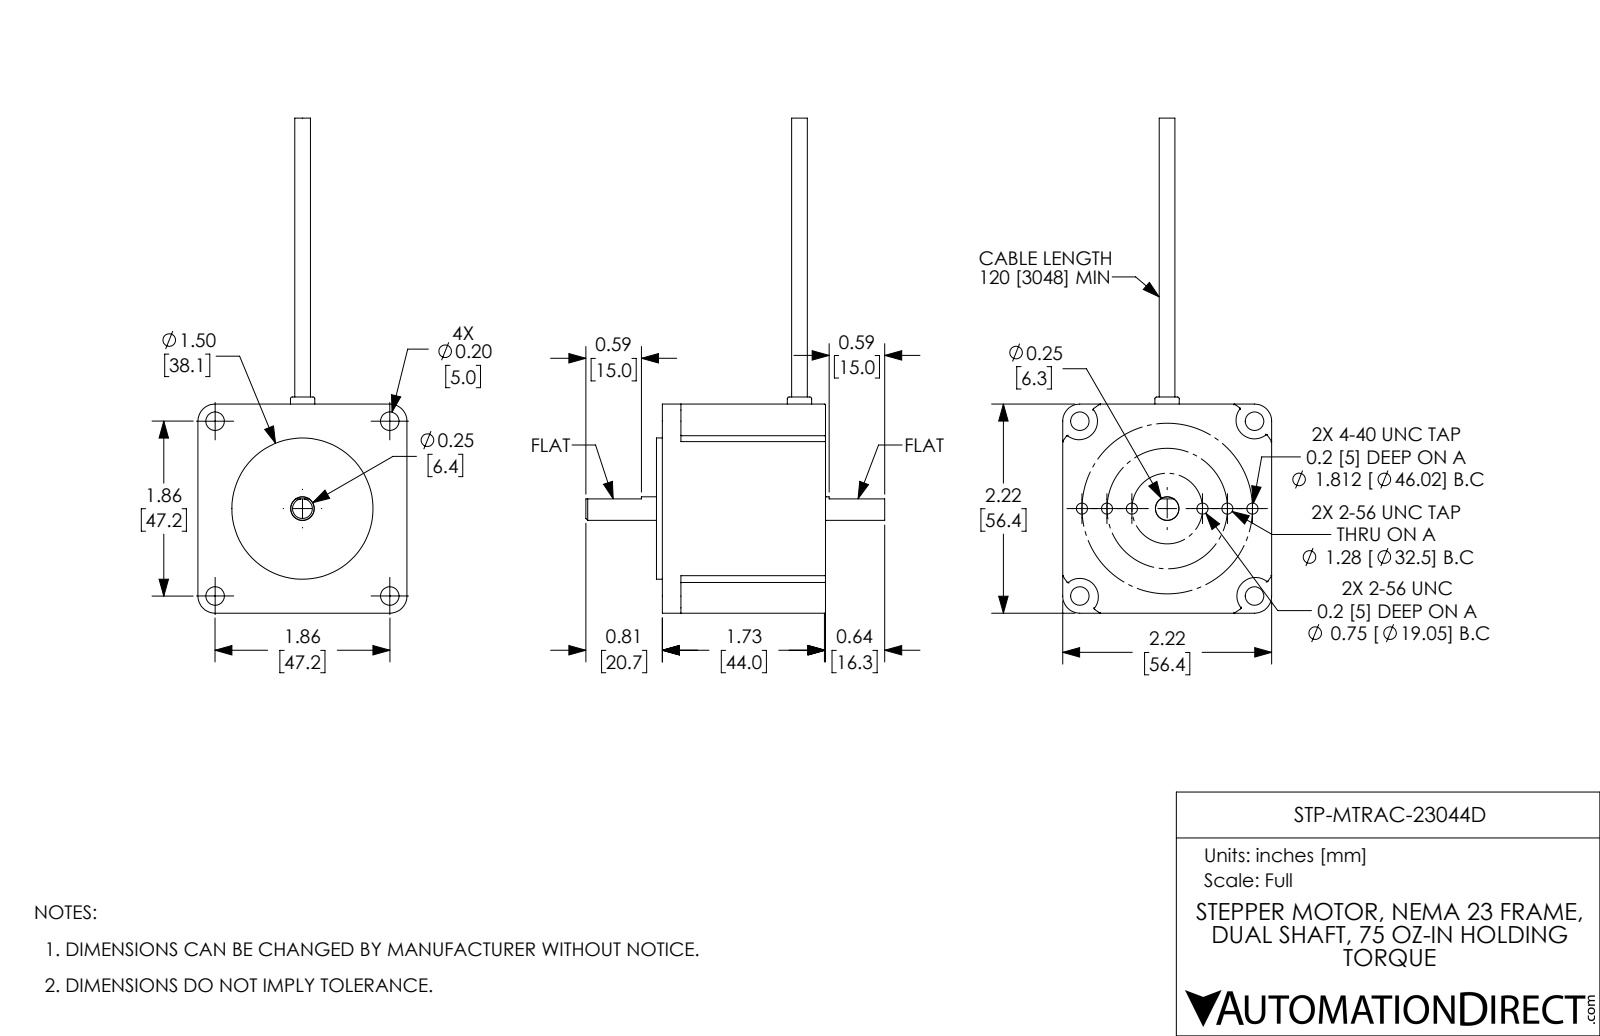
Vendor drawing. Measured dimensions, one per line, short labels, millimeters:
name: STP-MTRAC-23044D from HT23-552D-CAA r1 COORDS 1 mod1
written by: SolidWorks 2017 (AUTOMOTIVE_DESIGN)
unit: mm
bodies: 1 solid, 152 faces (25 planar, 62 cylindrical, 65 other)
size: 133.5 × 80.65 × 56.4
volume: 130 515 mm³; area: 18 366 mm²
holes: 6× ⌀3, 4× ⌀5
bosses: 1× ⌀38.1, 1× ⌀6.58, 1× ⌀6.35, 1× ⌀4.23
rounds: 12× R0.25, 4× R4.6, 4× R5, 1× R33.5
face distances: 56.4, 44, 45.6, 1.6, 5, 39, 6.6, 30.82, 25.58, 34
hole spacings: 23.58, 24.68, 40.63, 46.27, 47.14, 52.2, 6.76, 27.43
